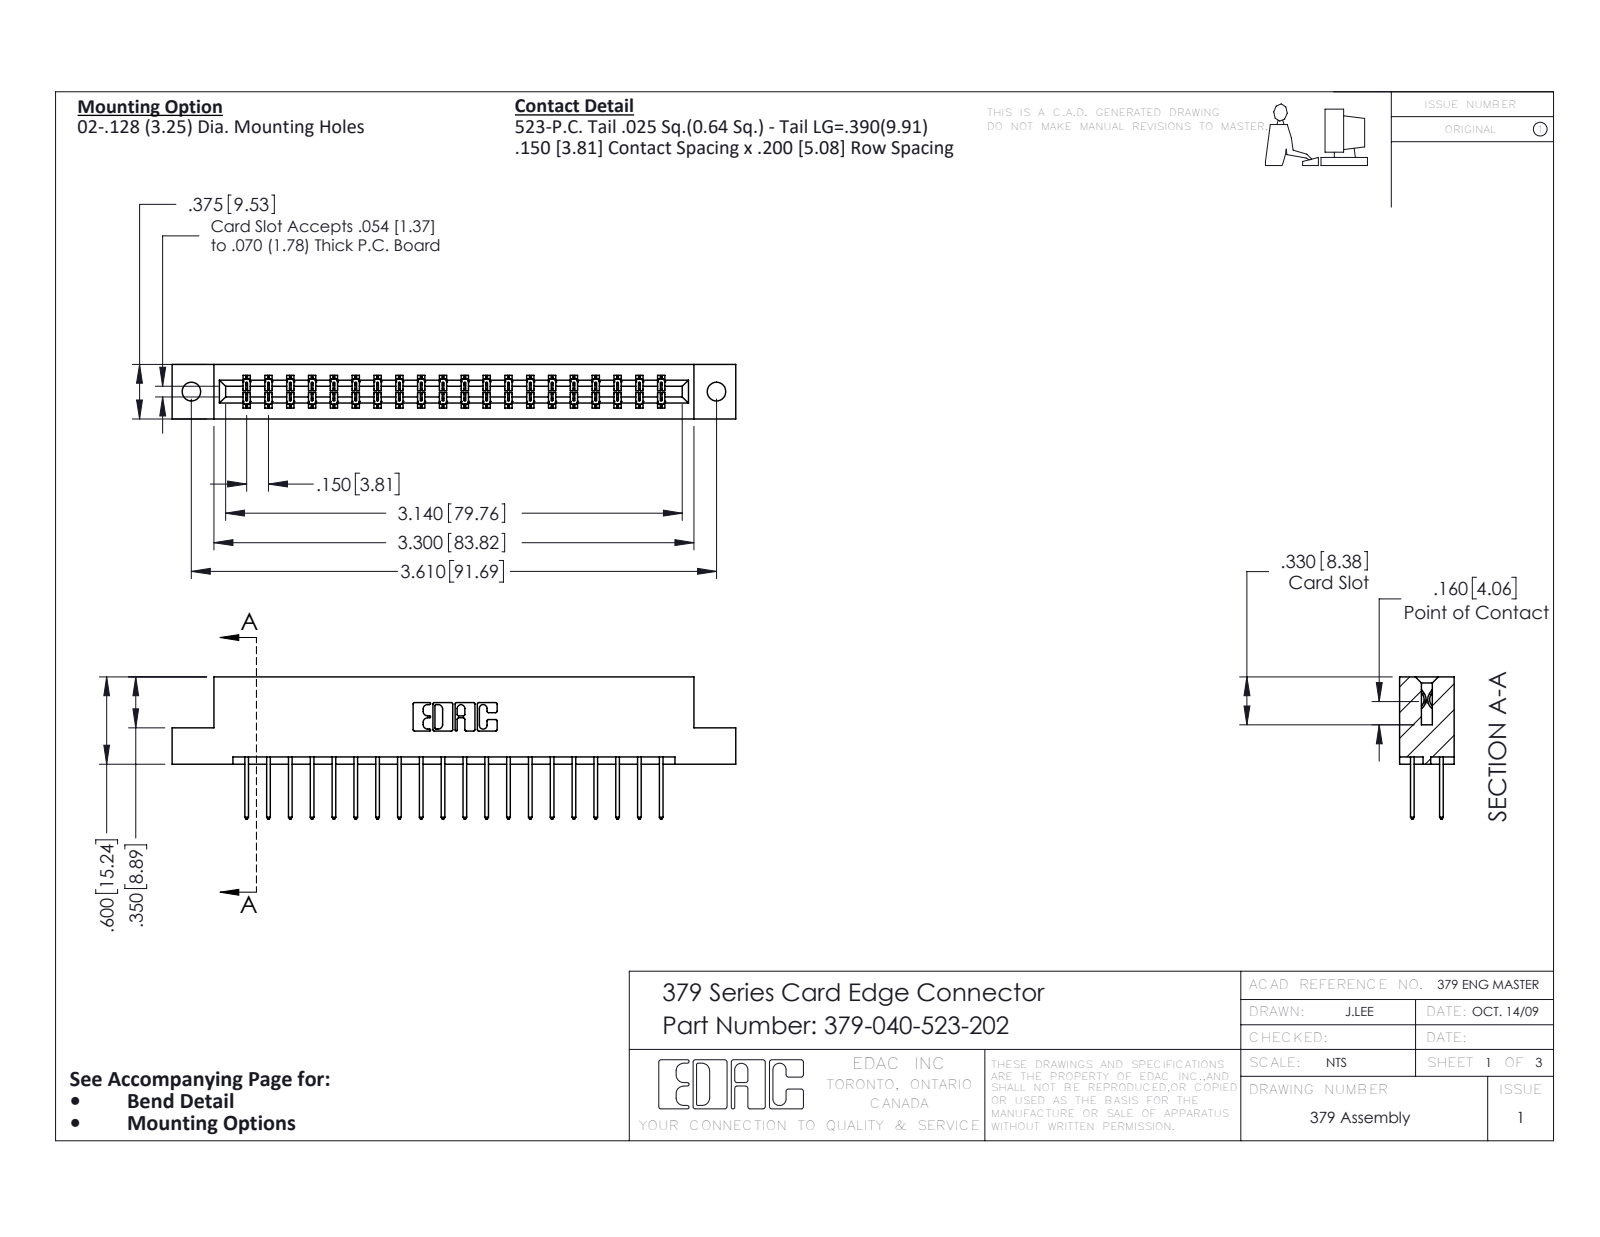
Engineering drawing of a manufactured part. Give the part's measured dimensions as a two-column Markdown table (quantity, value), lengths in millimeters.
| quantity | value |
| --- | --- |
| part name | 379-040-523-202; 379 Part_Flush - .128 Dia; 345-292-001_345-293-123 |
| STEP written by | SolidWorks 2016 (CONFIG_CONTROL_DESIGN) |
| units | millimeters |
| bodies | 41 solids, 2194 faces (1510 planar, 684 cylindrical, 0 other) |
| overall size | 98.4 × 24.8 × 9.5 |
| volume | 10 300 mm³ |
| surface area | 11 430 mm² |
| round holes (diameter × count) | 3.3 × 2 |
| partial cylindrical surfaces (radius × count) | 0.2 × 60, 0.3 × 40, 0.3 × 22, 0.2 × 6, 0.8 × 6, 0.7 × 3, 0.4 × 2, 0.6 × 2 |
| main face-to-face distances | 7.6, 1.9, 9.5, 5.1, 15.2, 7, 5.7, 2.5, 3.8, 0.6 |
| hole center spacings | 91.7 |
